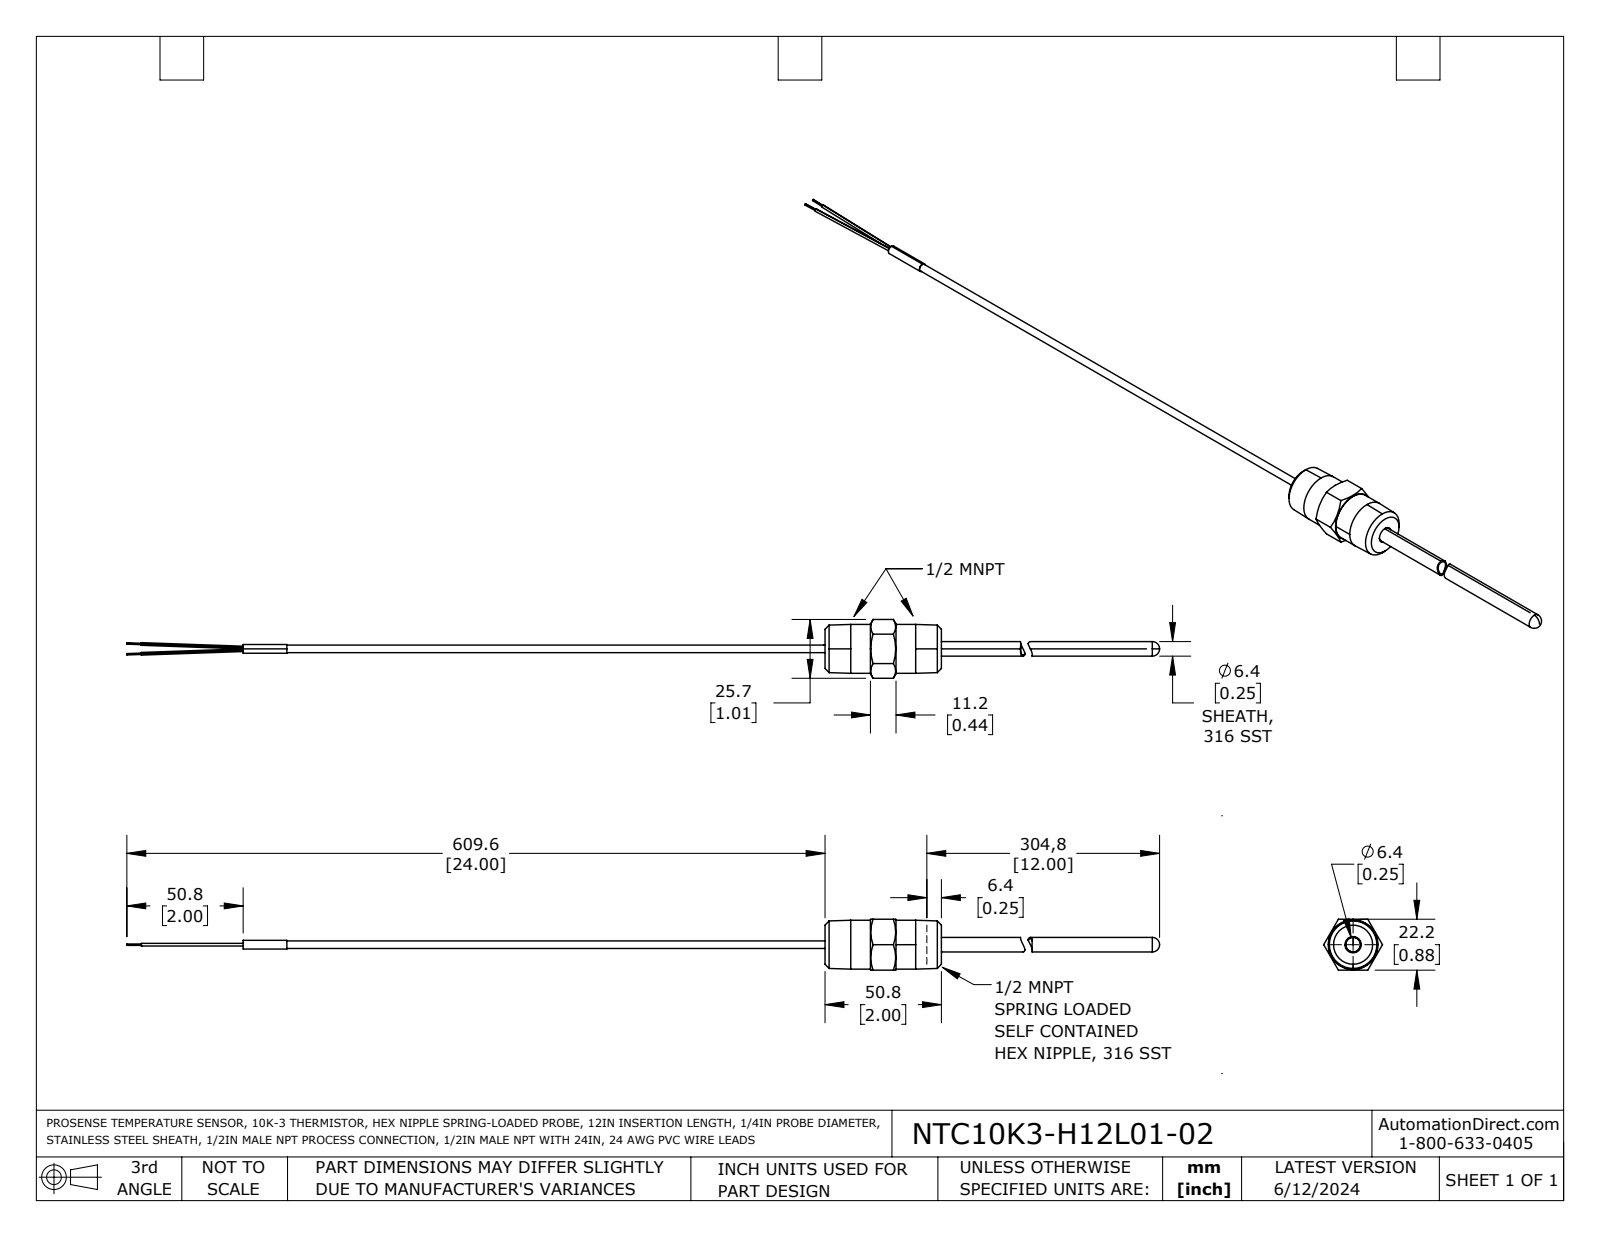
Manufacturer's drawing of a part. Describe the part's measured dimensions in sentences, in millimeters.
The part is named "NTC10K3-H12L01-02 fxt". Its 3-D file was written by "SolidWorks 2021 (AUTOMOTIVE_DESIGN)". It is 2 solids with 74 faces: 24 planar, 22 cylindrical and 28 other. Overall it measures 653.9 by 25.7 by 22.2 millimeters. Its volume is 19 390 cubic millimeters and its surface area 20 410 square millimeters. Round holes: 1 of diameter 3.3, 1 of diameter 5.3, 1 of diameter 6.6, 1 of diameter 11.1, 1 of diameter 11.8. Round bosses or shafts: 1 of diameter 21.3, 1 of diameter 11.6, 1 of diameter 6.4, 1 of diameter 3.8, 1 of diameter 3.3. The main face-to-face distances are 22.2, 50.8, 2.7, 48.1, 2.5, 50.6, 19.8, 31, 343.5, 343.4.
